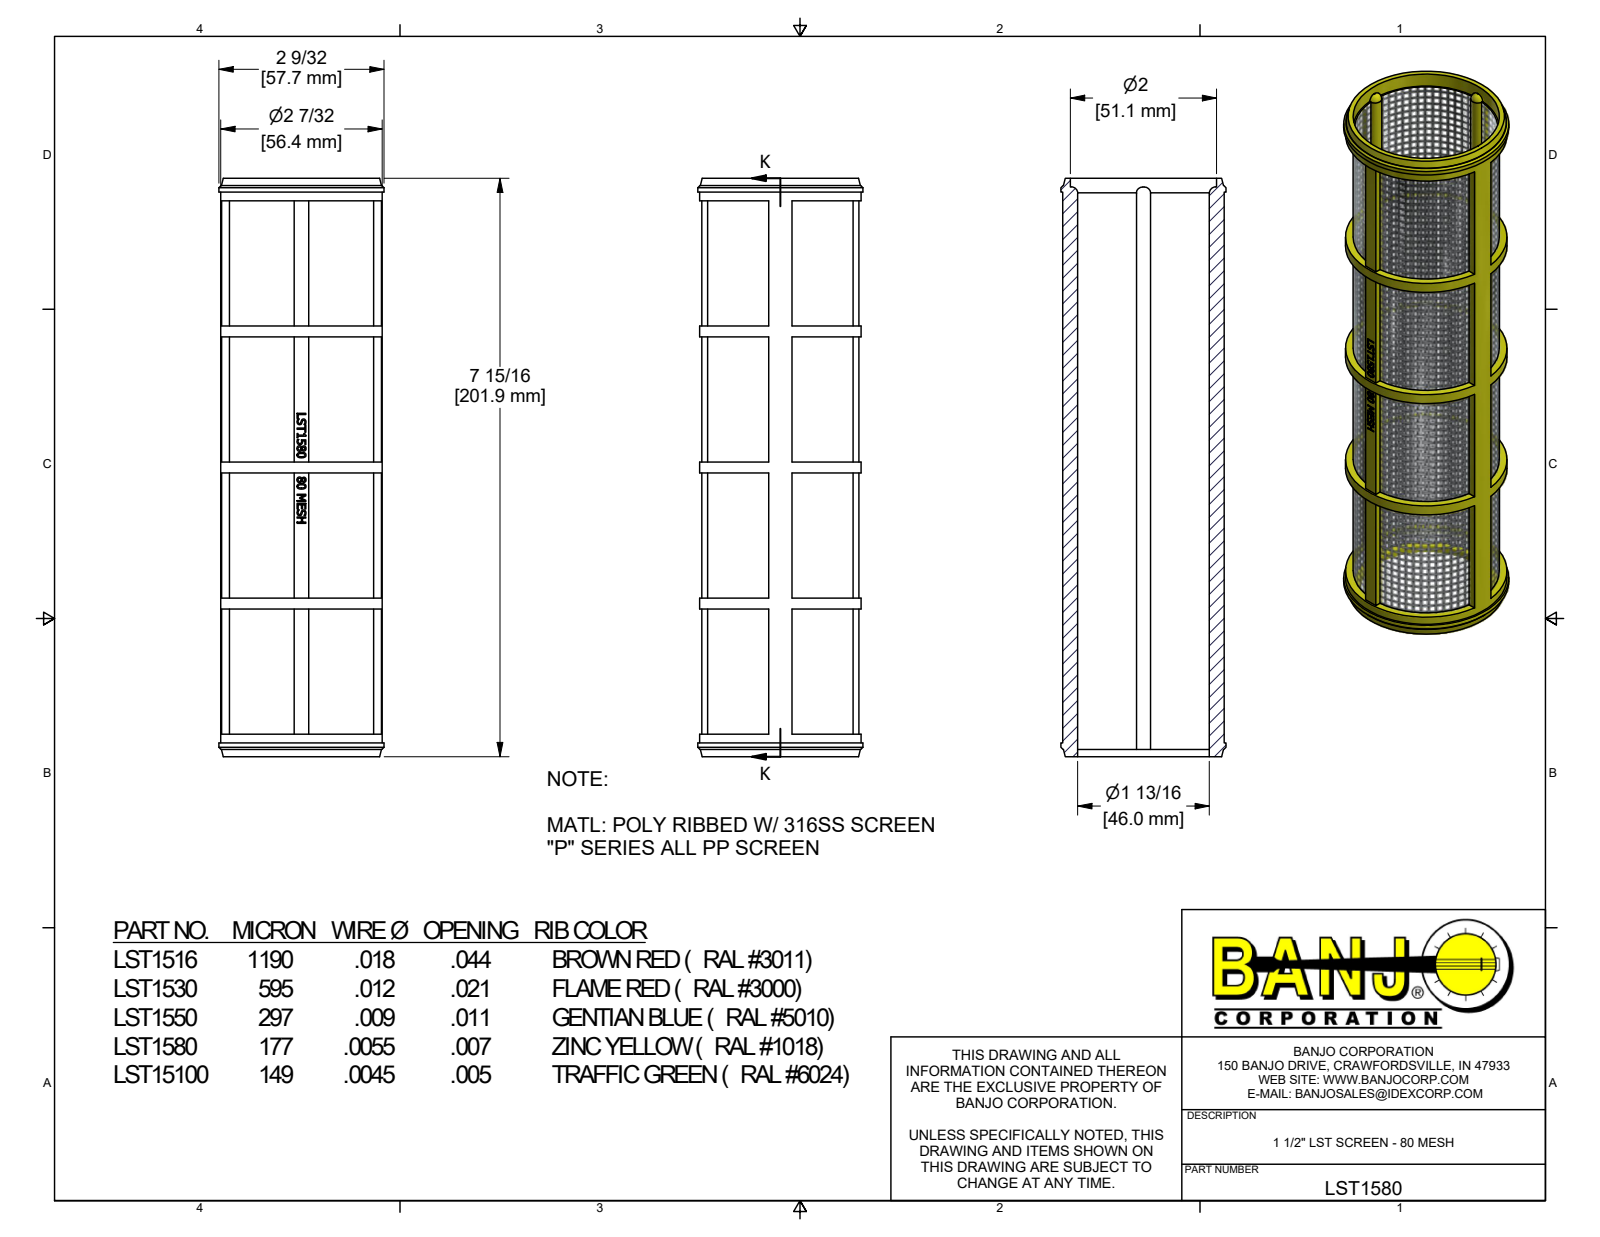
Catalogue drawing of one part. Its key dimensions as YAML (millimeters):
part_name: "LST1580"
step_written_by: "Autodesk Inventor 2019 (AUTOMOTIVE_DESIGN)"
units: millimeters
bodies: {solids: 1, faces: 471, planar: 318, cylindrical: 29, other: 124}
overall_size: [201.9, 57.7, 57.7]
volume: 45610
surface_area: 74320
round_holes:
  - {diameter: 46, count: 1}
  - {diameter: 50, count: 1}
round_bosses_or_shafts:
  - {diameter: 57.7, count: 1}
  - {diameter: 56.4, count: 1}
  - {diameter: 51.1, count: 1}
partial_cylinders:
  - {radius: 2.5, count: 4}
face_to_face_distances: [47.5, 23.4, 31.5, 95, 43.7, 91.2, 3.8, 8.1, 54.9, 5.1]
